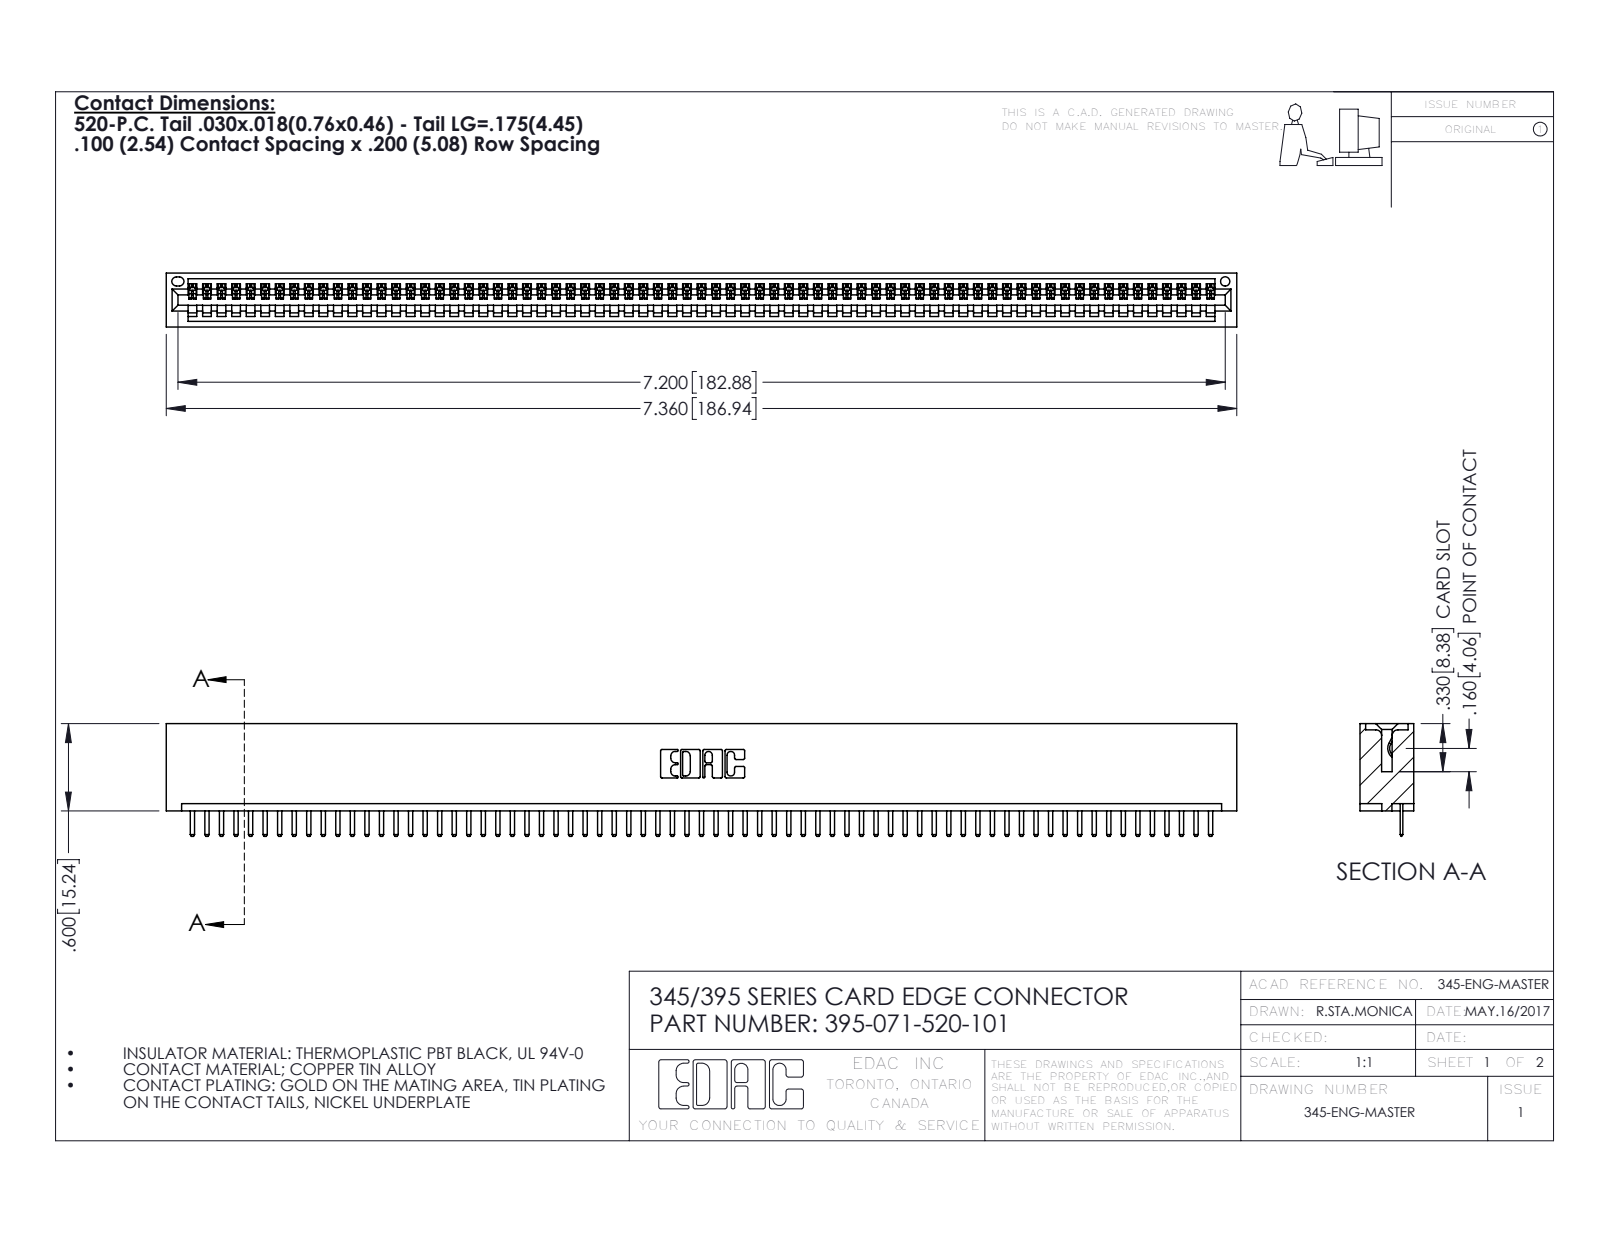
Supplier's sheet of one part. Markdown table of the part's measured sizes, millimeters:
| quantity | value |
| --- | --- |
| part name | 395-071-520-101; 345-292-001_345-293-120; 345 Part_No Mounting Lugs |
| STEP written by | SolidWorks 2016 (CONFIG_CONTROL_DESIGN) |
| units | millimeters |
| bodies | 72 solids, 4520 faces (3058 planar, 1462 cylindrical, 0 other) |
| overall size | 186.9 × 19.7 × 9.4 |
| volume | 18 370 mm³ |
| surface area | 24 340 mm² |
| round holes (diameter × count) | 1.6 × 1 |
| partial cylindrical surfaces (radius × count) | 0.3 × 144, 0.2 × 142, 0.3 × 22, 0.2 × 6, 0.8 × 6, 0.7 × 3, 0.8 × 2, 1 × 2 |
| main face-to-face distances | 7.6, 1.8, 9.4, 5.1, 2.5, 6.9, 0.6, 5.7, 1.8, 3.8 |
